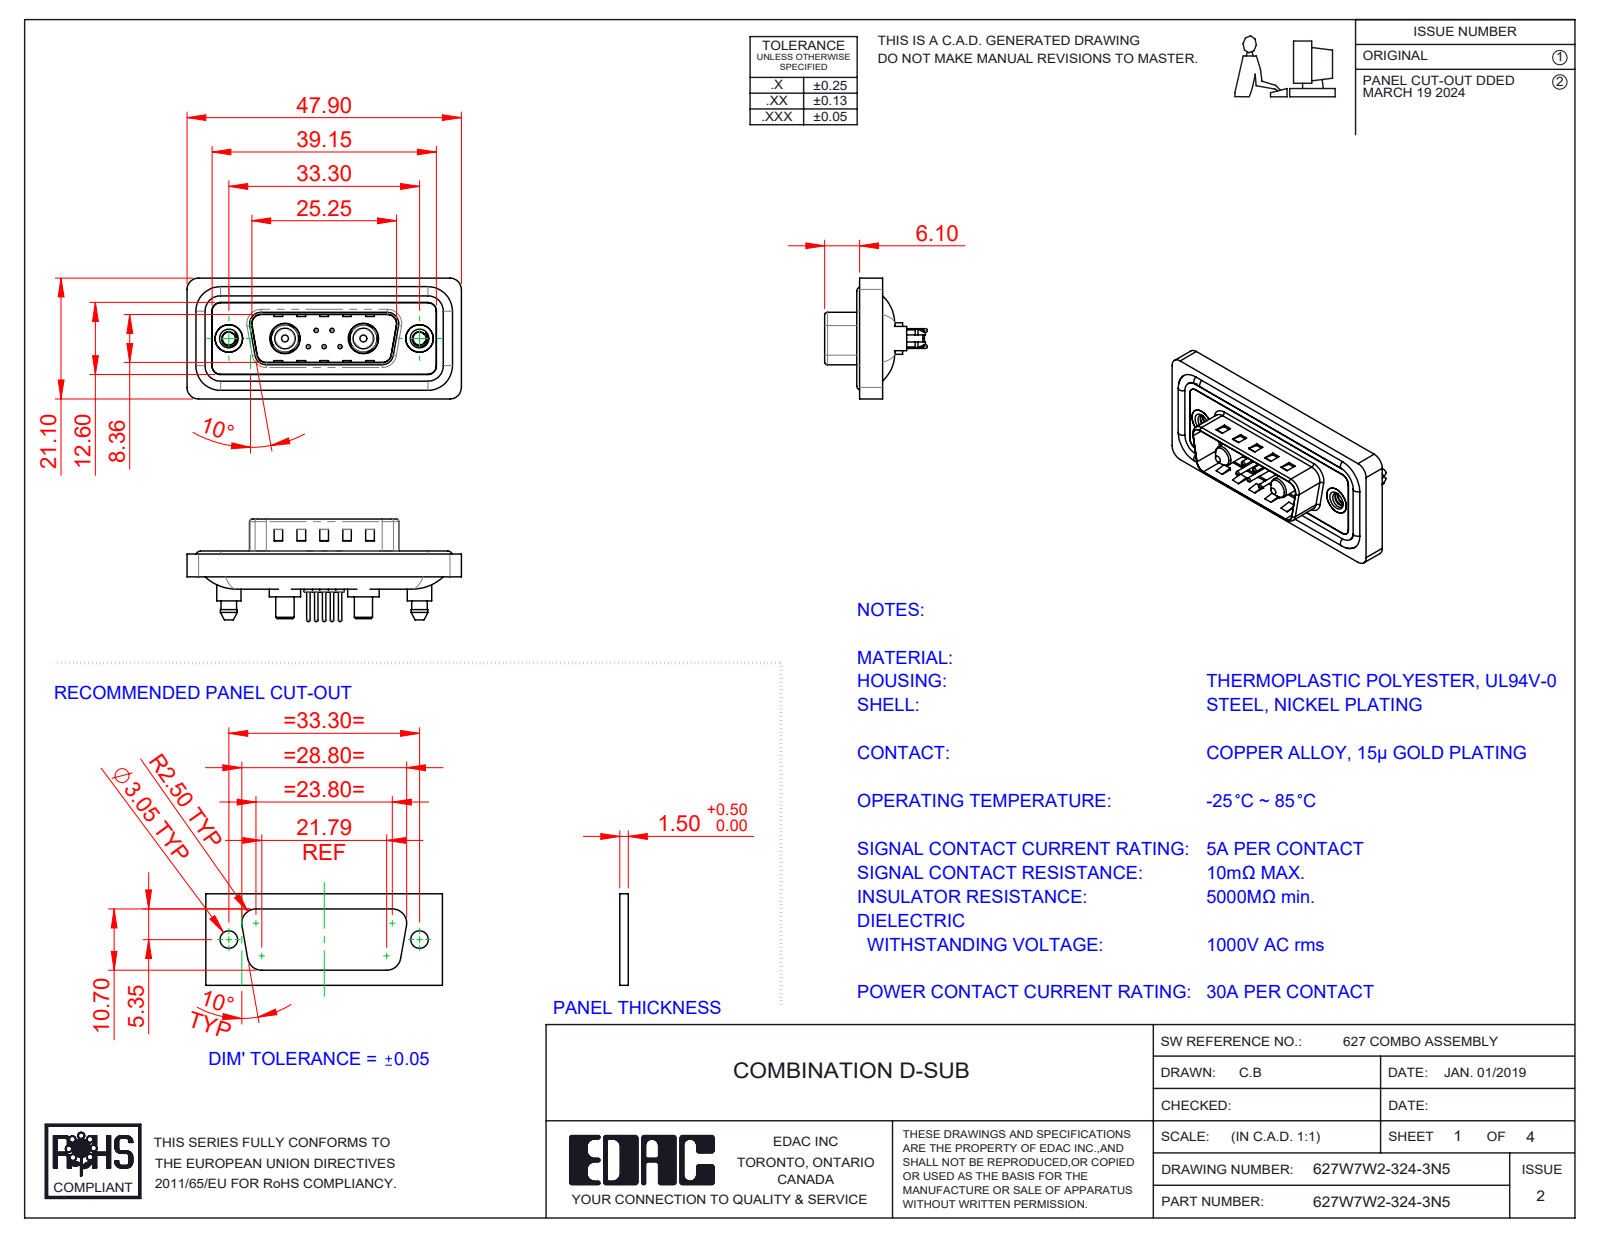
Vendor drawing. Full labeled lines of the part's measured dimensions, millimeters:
Part name (STEP PRODUCT): 627Combo Waterproof Housing_15 Contacts; 627Combo Shell Rear_15 Contacts; 627W7W2-324-3N5; 627Combo Housing_7W2 (+5 more)
STEP written by: SolidWorks 2023 (CONFIG_CONTROL_DESIGN)
Units: millimetres
Bodies: 16 solids, 760 faces (248 planar, 324 cylindrical, 188 other)
Overall size (bounding box): 47.9 × 21.1 × 17.9
Volume: 5 665 mm³ · Surface area: 9 135 mm²
Round holes (diameter × count): ⌀0.75 ×5, ⌀1.6 ×5, ⌀2 ×5, ⌀2.26 ×2, ⌀4 ×2, ⌀4.8 ×2, ⌀4.85 ×2, ⌀5 ×2, ⌀5.3 ×2
Round bosses / shafts (diameter × count): ⌀1.5 ×5, ⌀0.6 ×5, ⌀1.6 ×4, ⌀5.5 ×2, ⌀5.4 ×2, ⌀5.2 ×2, ⌀4.9 ×2, ⌀4.75 ×2
Partial cylindrical surfaces — rounded edges, fillets, slot ends (radius × count): R1.5 ×28, R2 ×20, R1.6 ×10, R0.5 ×8, R0.25 ×4, R0.6 ×4, R0.65 ×4, R0.9 ×4
Main face-to-face distances: 0.4, 1.1, 1.5, 1.6, 0.5, 3.1, 2.9, 0.7, 4, 0.82
Hole centre spacings: 3.16, 2.77, 9.8, 23.5, 4.31, 4.33, 5.03, 5.04
